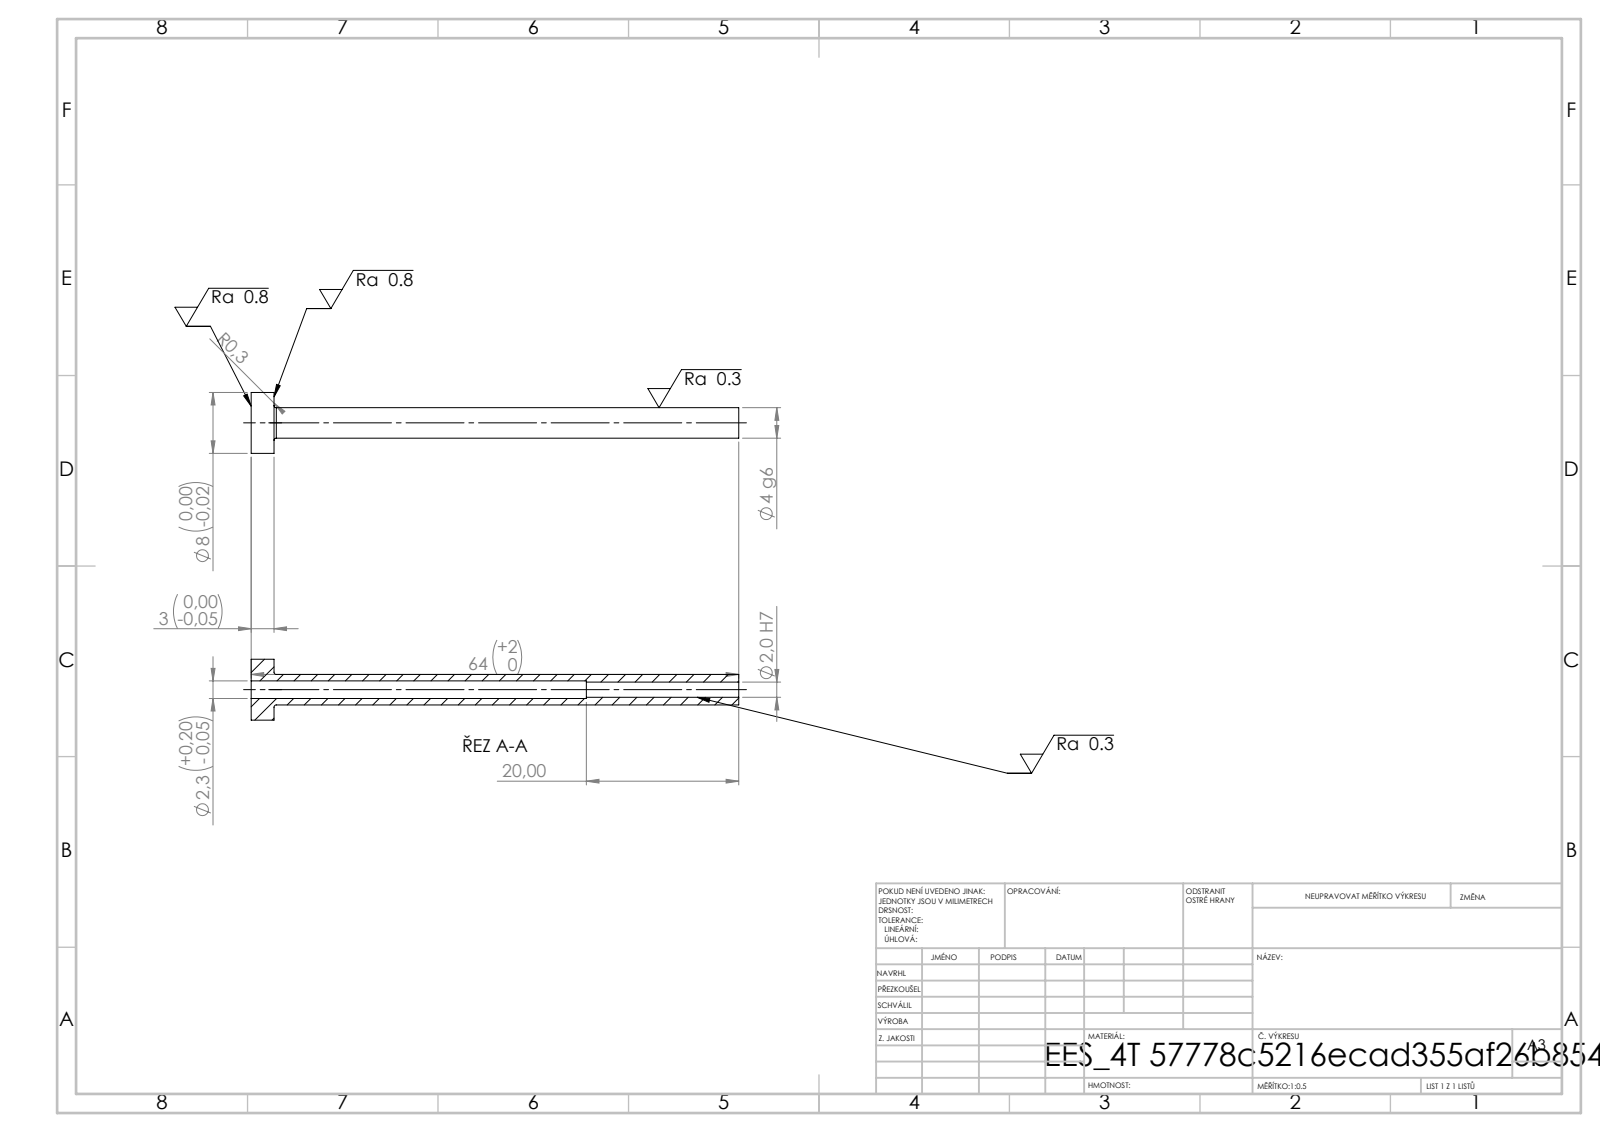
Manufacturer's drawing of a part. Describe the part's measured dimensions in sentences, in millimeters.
Its 3-D file was written by "SolidWorks 2019 (CONFIG_CONTROL_DESIGN)". It is 1 solid with 14 faces: 4 planar, 8 cylindrical and 2 other. Overall it measures 64 by 8 by 8 millimeters. Its volume is 672 cubic millimeters and its surface area 1 378 square millimeters. Round holes: 1 of diameter 2, 1 of diameter 2.3. Round bosses or shafts: 1 of diameter 8, 1 of diameter 4. The main face-to-face distances are 3, 64, 61, 44, 41, 20.
